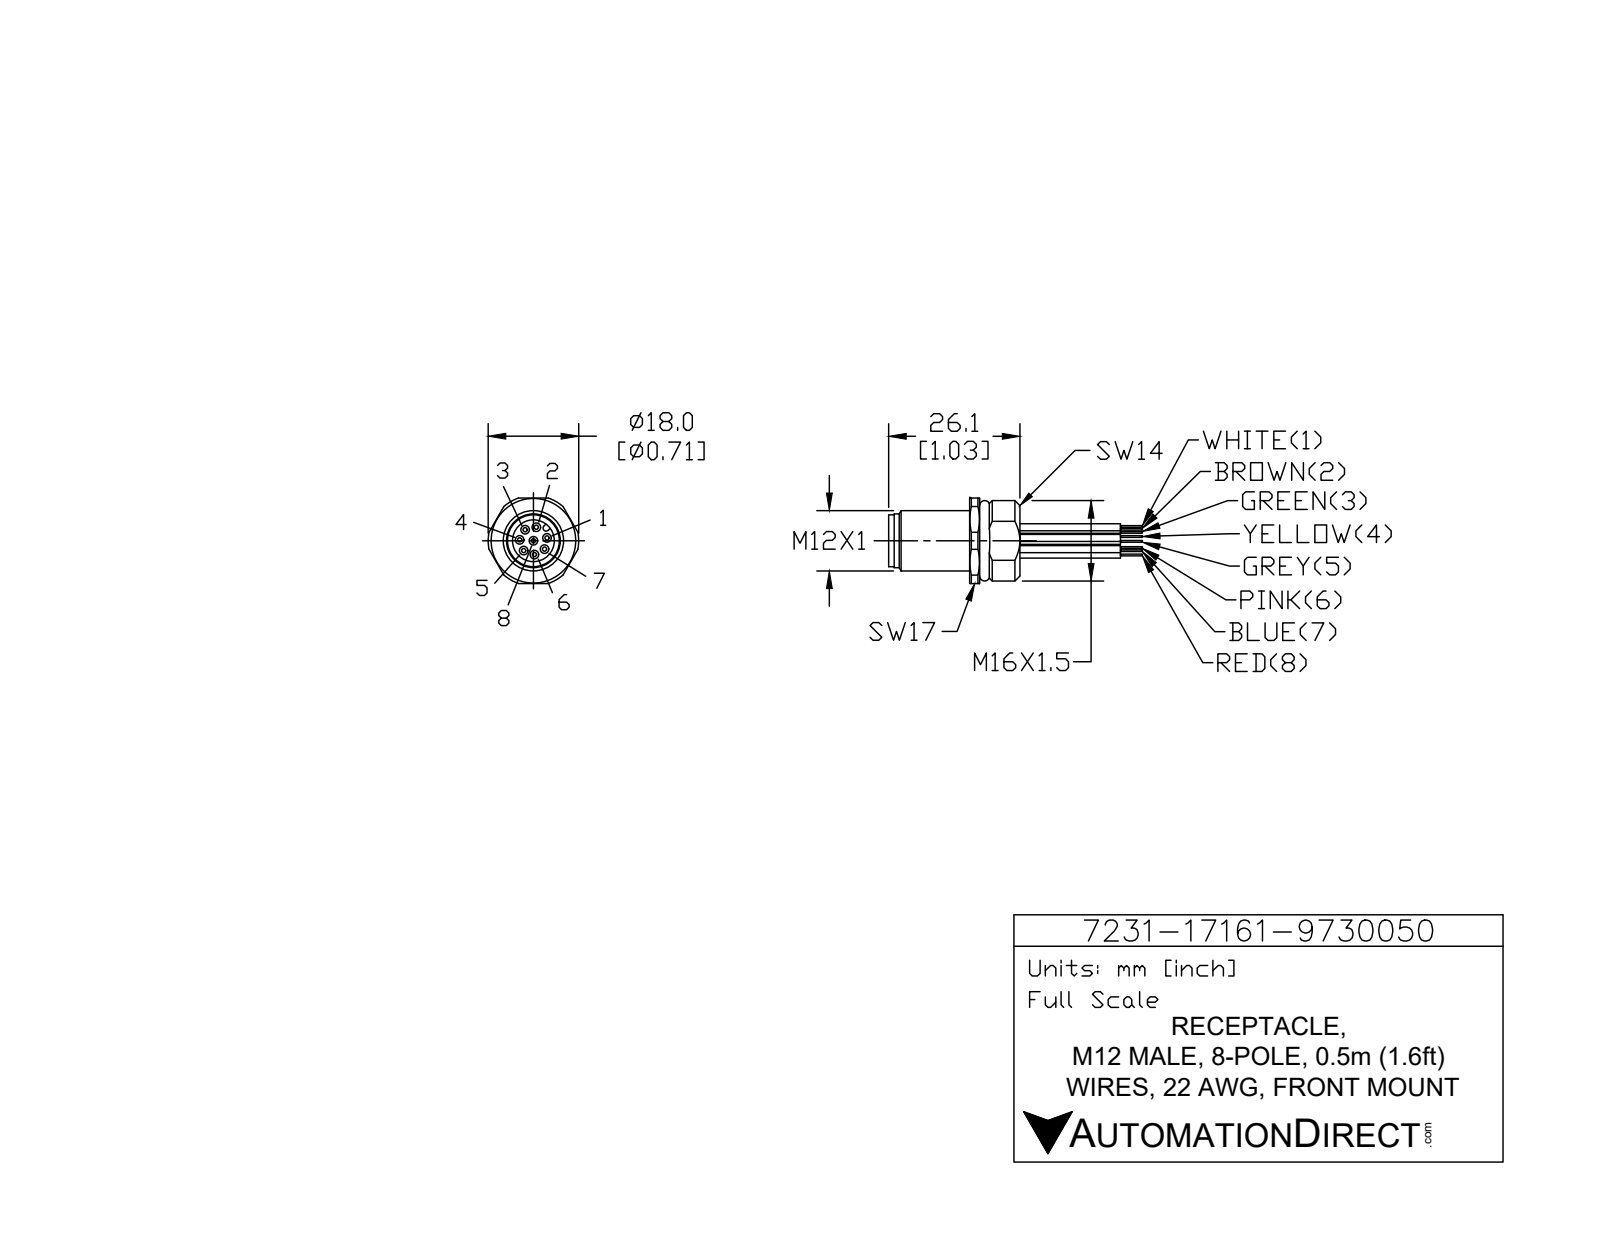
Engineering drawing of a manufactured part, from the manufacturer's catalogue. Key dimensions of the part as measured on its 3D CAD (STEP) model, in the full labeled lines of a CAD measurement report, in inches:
Part name (STEP PRODUCT): 7231-17161-9730050
STEP written by: SolidWorks 2015 (AUTOMOTIVE_DESIGN)
Units: inches
Bodies: 1 solid, 140 faces (42 planar, 68 cylindrical, 30 other)
Overall size (bounding box): 1.815 × 0.709 × 0.669
Volume: 0.209 in³ · Surface area: 4.363 in²
Round holes (diameter × count): ⌀0.067 ×8, ⌀0.327 ×1, ⌀0.512 ×1
Round bosses / shafts (diameter × count): ⌀0.055 ×8, ⌀0.032 ×8, ⌀0.472 ×1, ⌀0.421 ×1, ⌀0.406 ×1
Partial cylindrical surfaces — rounded edges, fillets, slot ends (radius × count): R0.024 ×1, R0.315 ×1, R0.354 ×1
Main face-to-face distances: 0.354, 0.276, 0.079, 0.551, 0.669, 0.638, 0.362, 0.283, 0.35, 0.988
Hole centre spacings: 0.108, 0.163, 0.207, 0.214, 0.089, 0.09, 0.09, 0.183
